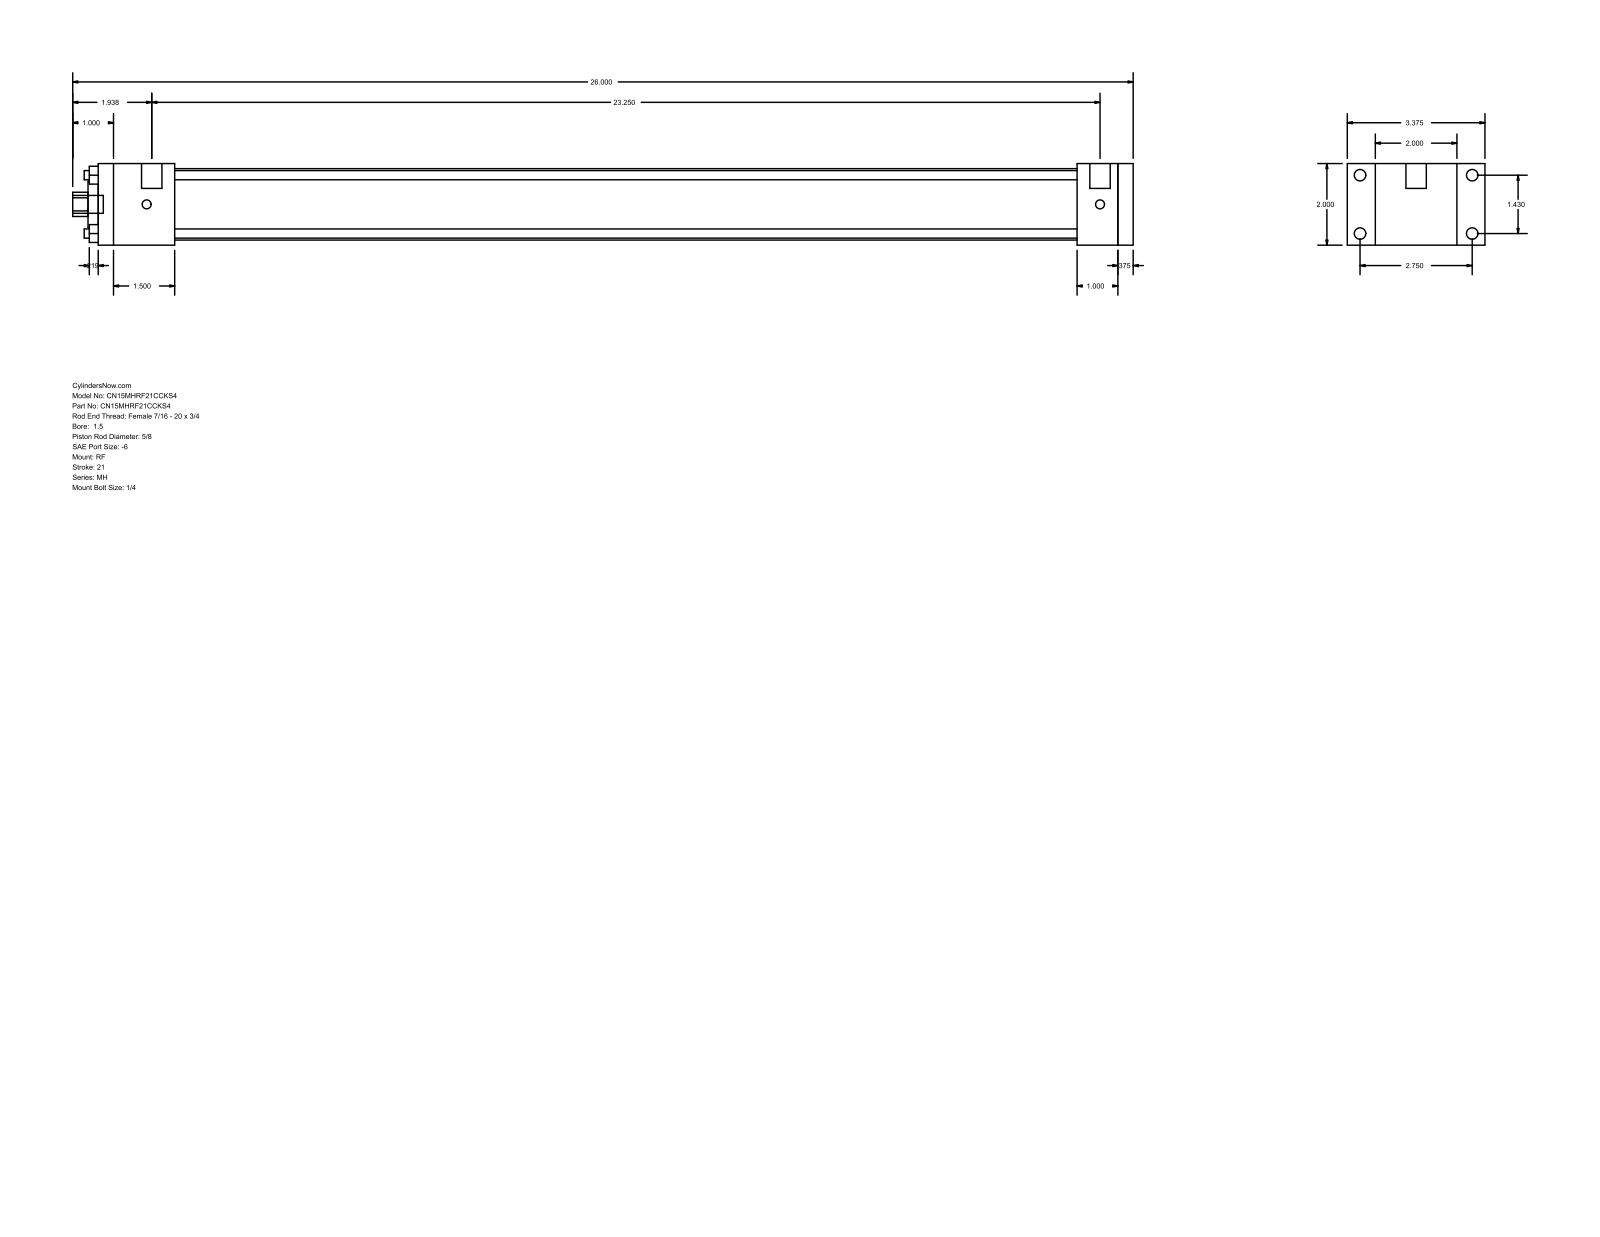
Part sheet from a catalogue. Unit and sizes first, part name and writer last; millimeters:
Units: millimetres
Overall size (bounding box): 660.4 × 85.72 × 50.8
Round holes (diameter × count): ⌀5.71 ×4, ⌀15.88 ×1, ⌀28.57 ×1, ⌀44.45 ×1
Round bosses / shafts (diameter × count): ⌀7.14 ×4, ⌀5.56 ×4, ⌀12.7 ×2, ⌀11.11 ×1
Partial cylindrical surfaces — rounded edges, fillets, slot ends (radius × count): R7.54 ×1
Main face-to-face distances: 50.8, 9.52, 635, 644.52, 17.46, 68.26, 609.6, 25.4, 34.92, 47.62
Hole centre spacings: 25.68, 36.32, 51.36
Bodies: 0 solids, 92 faces (64 planar, 28 cylindrical, 0 other)
Part name (STEP PRODUCT): MH_RF__0150_0.625
STEP written by: GSSL Pune (CONFIG_CONTROL_DESIGN)
